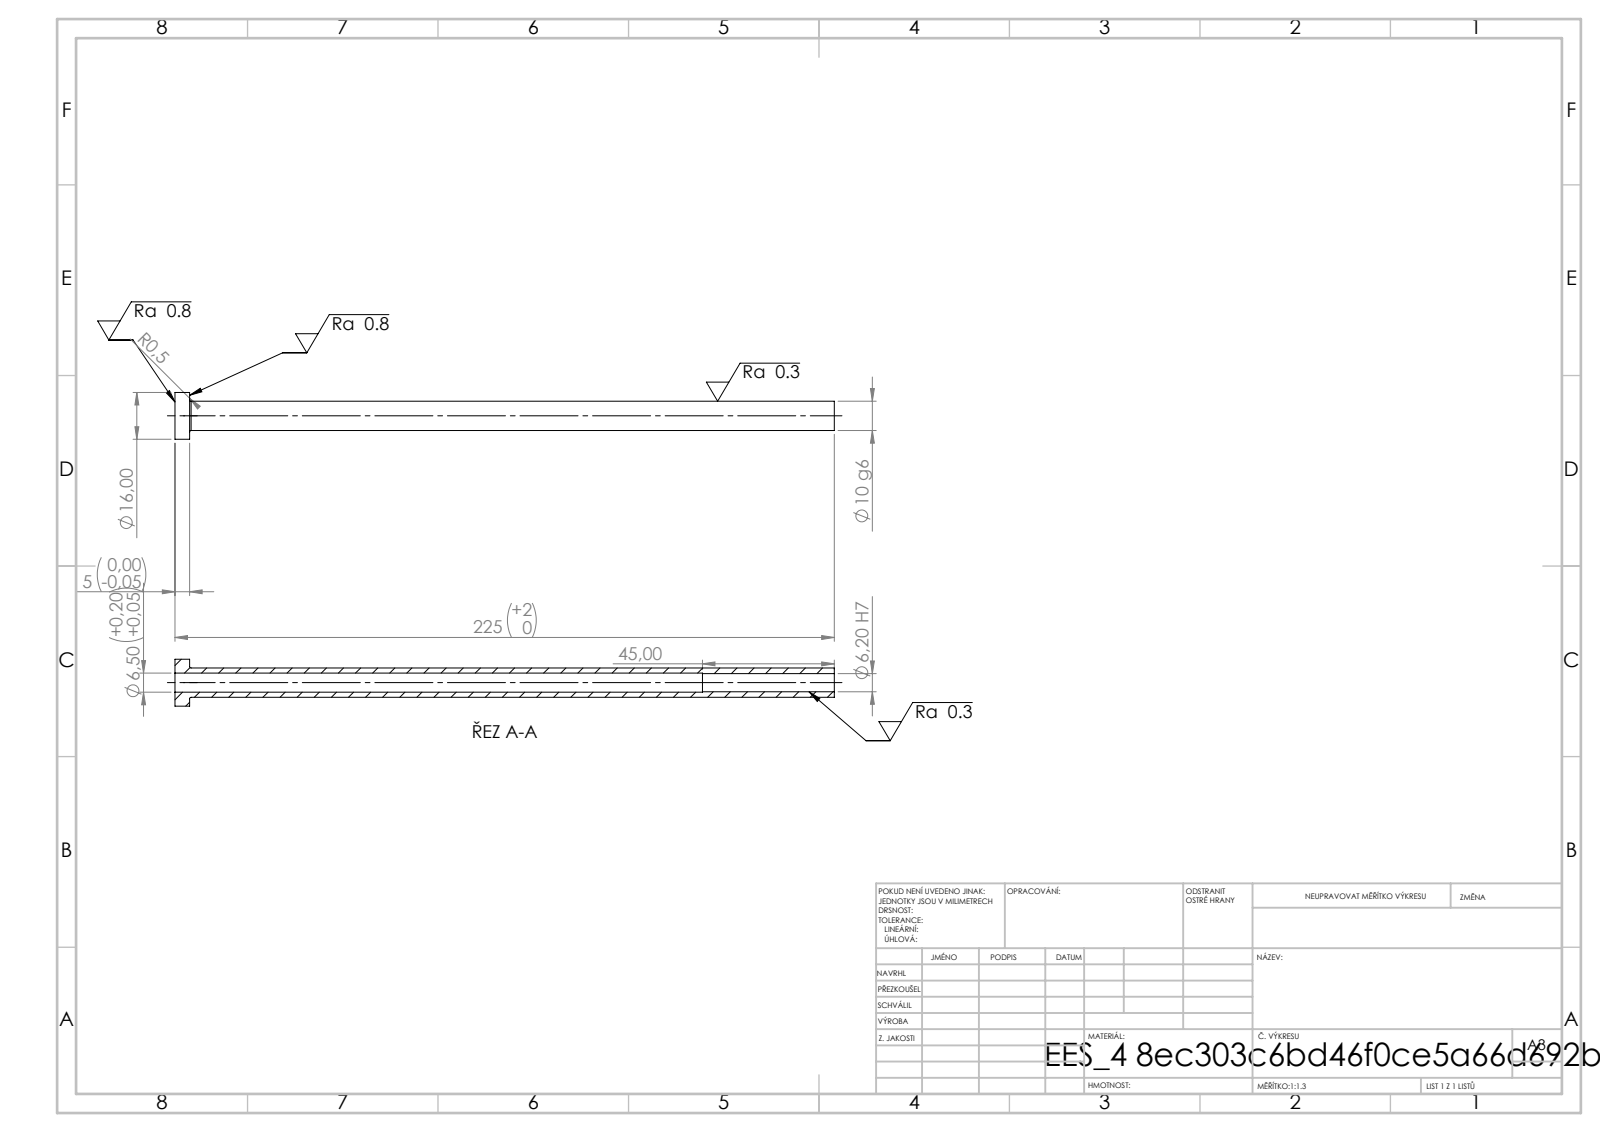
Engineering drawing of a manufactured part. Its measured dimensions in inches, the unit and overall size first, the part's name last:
Units: inches
Overall size (bounding box): 8.858 × 0.63 × 0.63
Round holes (diameter × count): ⌀0.244 ×1, ⌀0.256 ×1
Round bosses / shafts (diameter × count): ⌀0.63 ×1, ⌀0.394 ×1
Main face-to-face distances: 0.197, 8.858, 8.661, 7.087, 6.89, 1.772
Volume: 0.668 in³ · Surface area: 18.68 in²
Bodies: 1 solid, 14 faces (4 planar, 8 cylindrical, 2 other)
STEP written by: SolidWorks 2019 (CONFIG_CONTROL_DESIGN)
